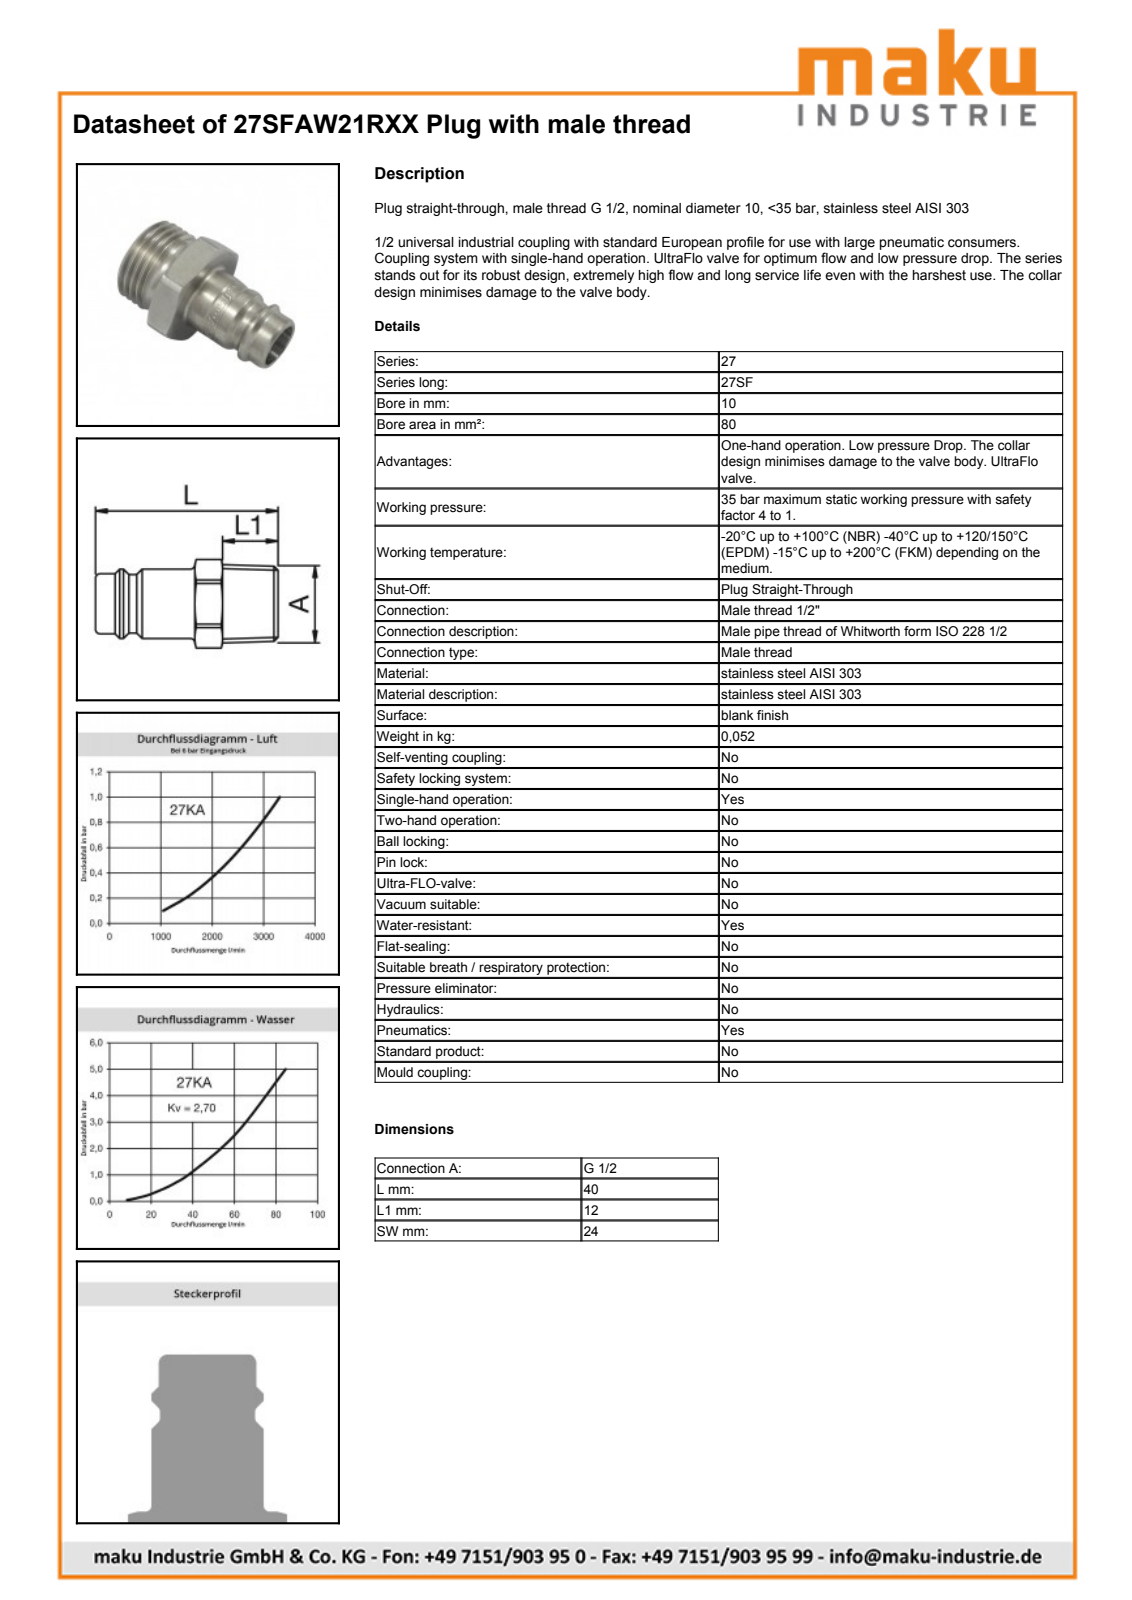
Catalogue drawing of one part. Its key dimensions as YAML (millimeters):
part_name: "D106026"
step_written_by: "Autodesk Inventor 2011 (AUTOMOTIVE_DESIGN)"
units: millimeters
bodies: {solids: 1, faces: 231, planar: 95, cylindrical: 36, other: 100}
overall_size: [40, 27.05, 24]
volume: 7030
surface_area: 4314
round_holes:
  - {diameter: 10, count: 1}
round_bosses_or_shafts:
  - {diameter: 20.95, count: 1}
  - {diameter: 15, count: 1}
  - {diameter: 14.5, count: 1}
  - {diameter: 13, count: 1}
  - {diameter: 12.65, count: 1}
partial_cylinders:
  - {radius: 7.15, count: 1}
  - {radius: 13.53, count: 1}
face_to_face_distances: [24, 6.5, 18.5, 12, 21.5, 28, 40, 15.78, 5.72, 12.22]
